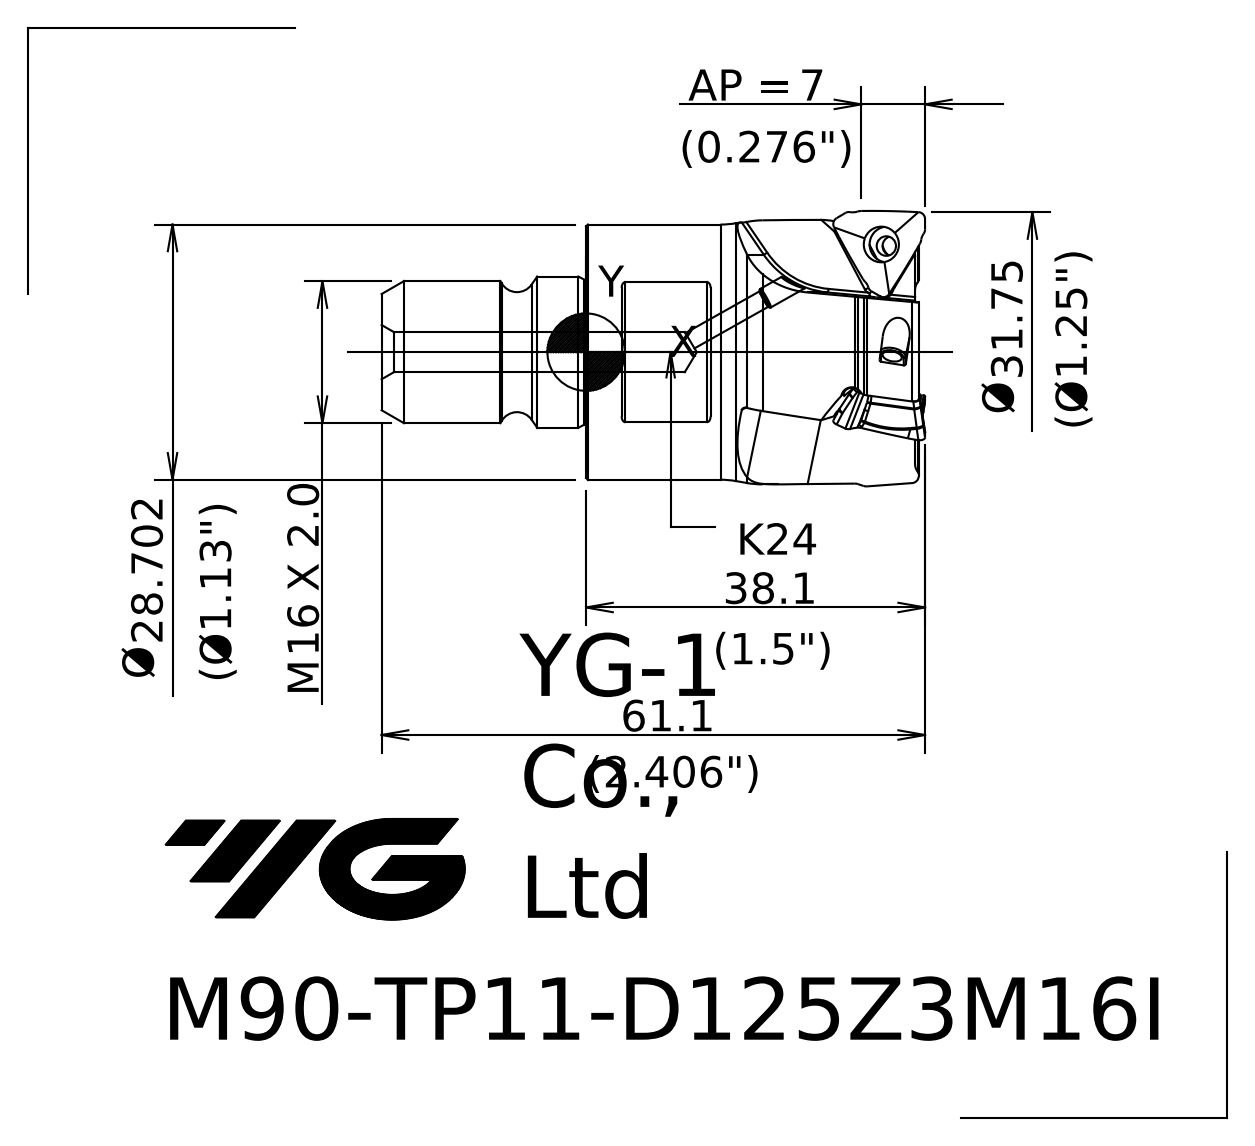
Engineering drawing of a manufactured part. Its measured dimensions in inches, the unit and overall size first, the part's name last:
Units: inches
Overall size (bounding box): 2.406 × 1.251 × 1.251
Round holes (diameter × count): ⌀0.059 ×1, ⌀0.177 ×1
Round bosses / shafts (diameter × count): ⌀1.171 ×1, ⌀1.13 ×1, ⌀0.669 ×1, ⌀0.628 ×1
Partial cylindrical surfaces — rounded edges, fillets, slot ends (radius × count): R0.016 ×4
Main face-to-face distances: 1.457, 0.945, 0.906, 2.362, 1.299, 0.394, 0.551, 0.157, 1.063, 0.016
Volume: 1.737 in³ · Surface area: 13.82 in²
Bodies: 1 solid, 66 faces (10 planar, 10 cylindrical, 46 other)
Part name (STEP PRODUCT): 10227DEC3C74p6d5
STEP written by: SIEMENS PLM Software NX 10.0 (AP203_CONFIGURATION_CONTROLLED_3D_DESIGN_OF_MECHANICAL_PARTS_AND_ASSEMBLIES_MIM_LF)
